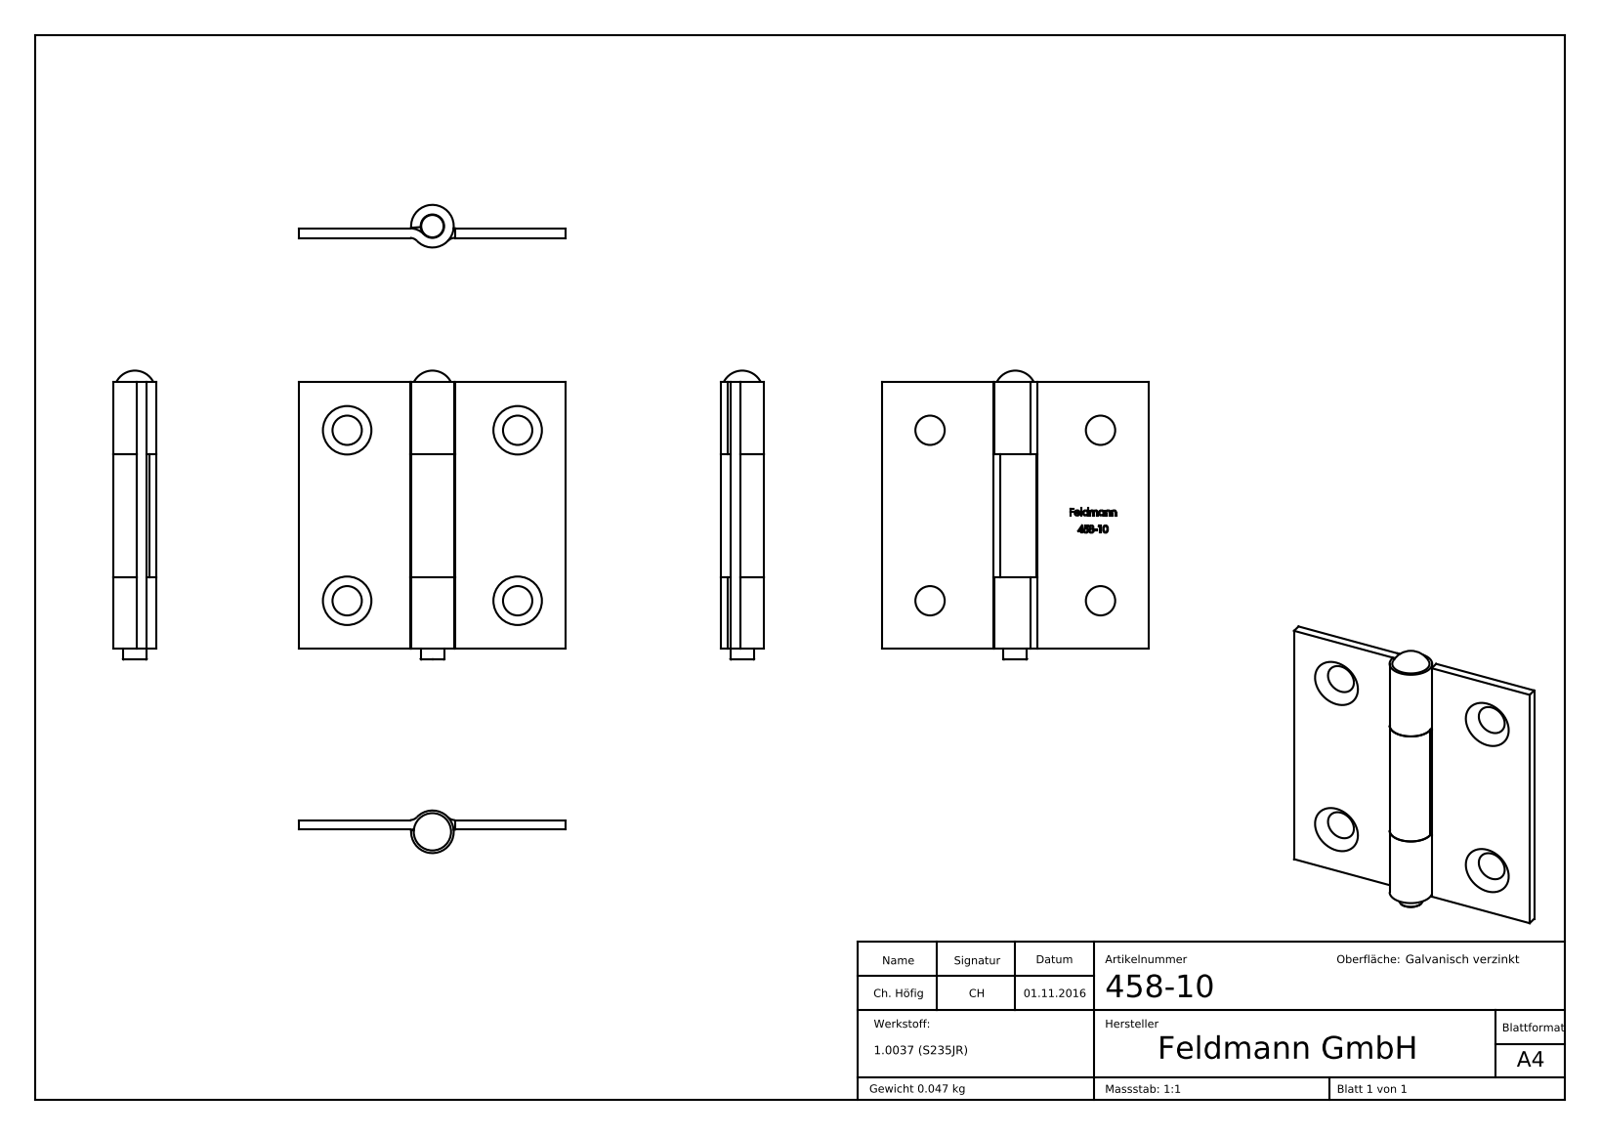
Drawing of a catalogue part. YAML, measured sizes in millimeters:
part_name: "458-10 Teil2; 458-10 Teil1; 458-10 Teil3; 458-10"
step_written_by: "SolidWorks 2018 (CONFIG_CONTROL_DESIGN)"
units: millimeters
bodies: {solids: 3, faces: 227, planar: 126, cylindrical: 13, other: 88}
overall_size: [54.2, 50, 8]
volume: 6033
surface_area: 7531
round_holes:
  - {diameter: 4.4, count: 1}
round_bosses_or_shafts:
  - {diameter: 8, count: 1}
partial_cylinders:
  - {radius: 1.8, count: 2}
  - {radius: 3.6, count: 2}
face_to_face_distances: [1.8, 50, 13.5, 36.5, 20.8, 29.2, 23, 8.4, 2, 15.5]
